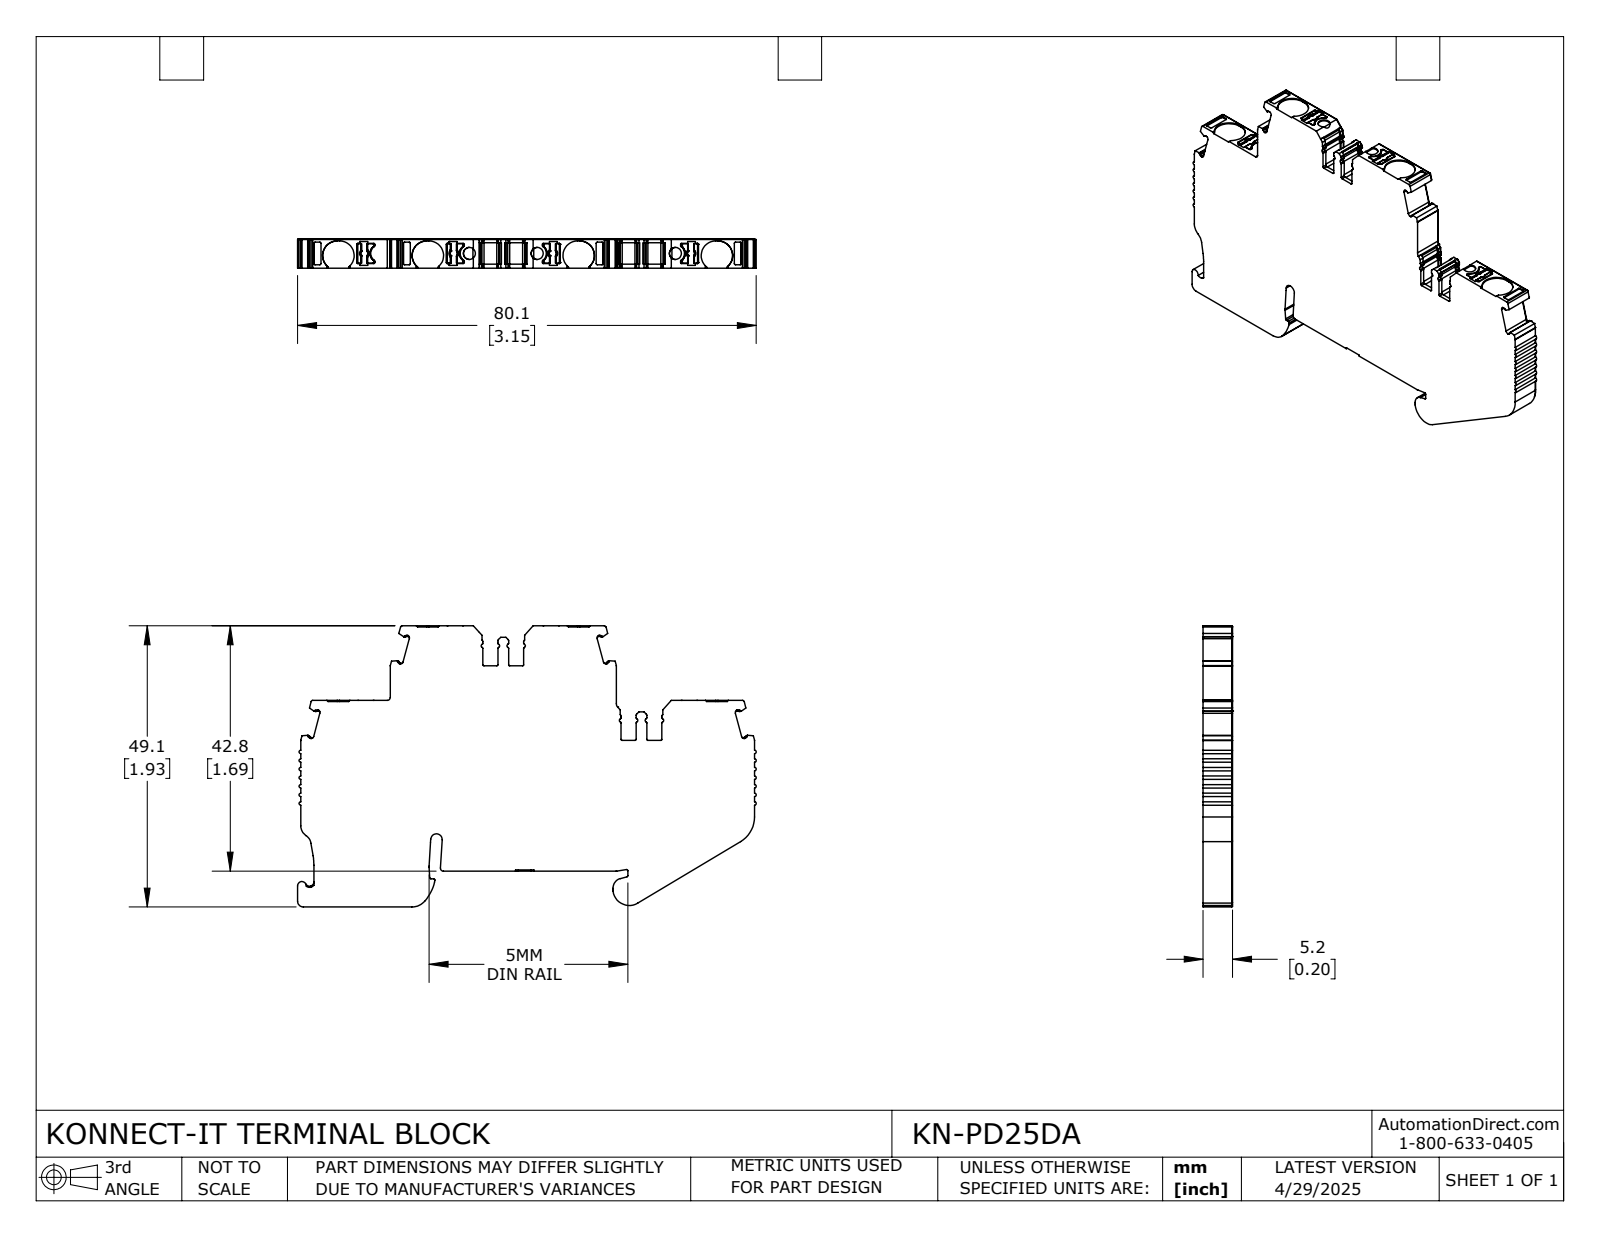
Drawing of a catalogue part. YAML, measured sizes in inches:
part_name: "KN-PD25DA"
step_written_by: "SolidWorks 2024 (CONFIG_CONTROL_DESIGN)"
units: inches
bodies: {solids: 1, faces: 979, planar: 470, cylindrical: 438, other: 71}
overall_size: [3.153, 1.933, 0.203]
volume: 0.889
surface_area: 11.63
round_holes:
  - {diameter: 0.083, count: 3}
partial_cylinders:
  - {radius: 0.008, count: 100}
  - {radius: 0.012, count: 57}
  - {radius: 0.004, count: 41}
  - {radius: 0.02, count: 21}
  - {radius: 0.016, count: 17}
  - {radius: 0.006, count: 16}
  - {radius: 0.024, count: 9}
  - {radius: 0.006, count: 8}
face_to_face_distances: [0.203, 0.512, 0.246, 1.678, 1.166, 1.924, 0.079, 1.412, 0.504, 0.95]
hole_center_spacings: [0.466, 0.95, 1.417]
